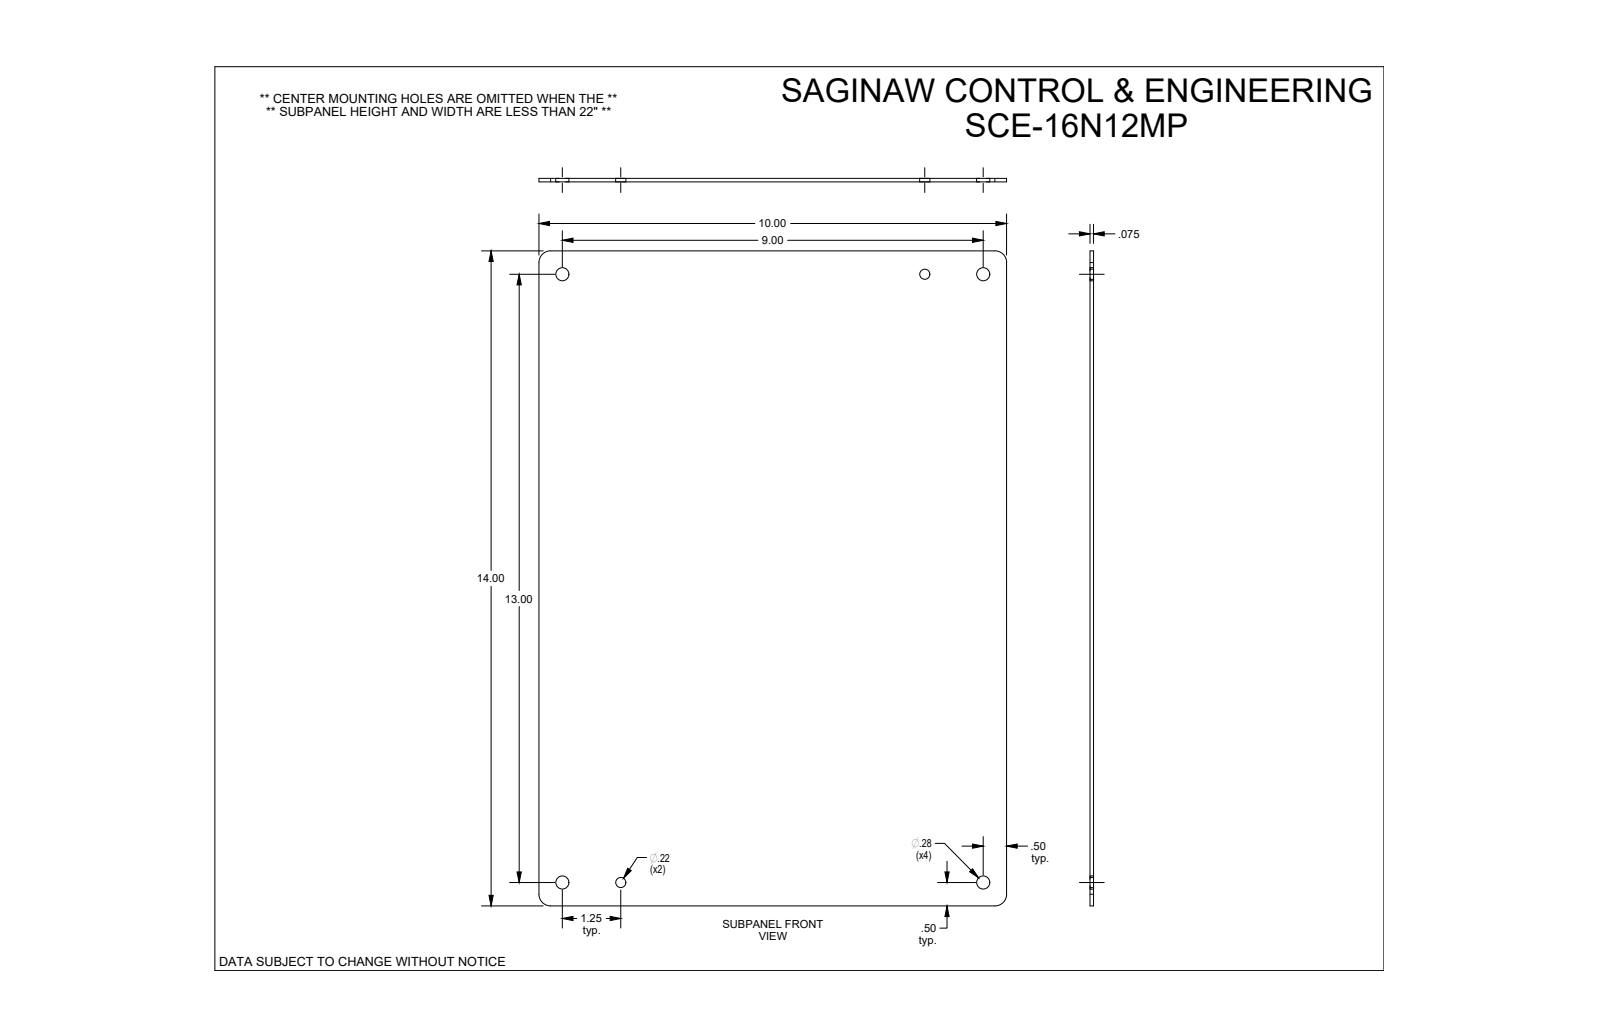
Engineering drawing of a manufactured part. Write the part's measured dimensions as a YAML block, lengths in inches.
part_name: "SCE-16N12MP"
step_written_by: "SolidWorks 2019 (CONFIG_CONTROL_DESIGN)"
units: inches
bodies: {solids: 1, faces: 16, planar: 6, cylindrical: 10, other: 0}
overall_size: [14, 10, 0.075]
volume: 10.47
surface_area: 283.2
round_holes:
  - {diameter: 0.281, count: 4}
  - {diameter: 0.218, count: 2}
partial_cylinders:
  - {radius: 0.25, count: 4}
face_to_face_distances: [0.075, 10, 14]
hole_center_spacings: [1.25, 7.75, 9, 13, 13.06, 15.135, 15.811, 14.534]
